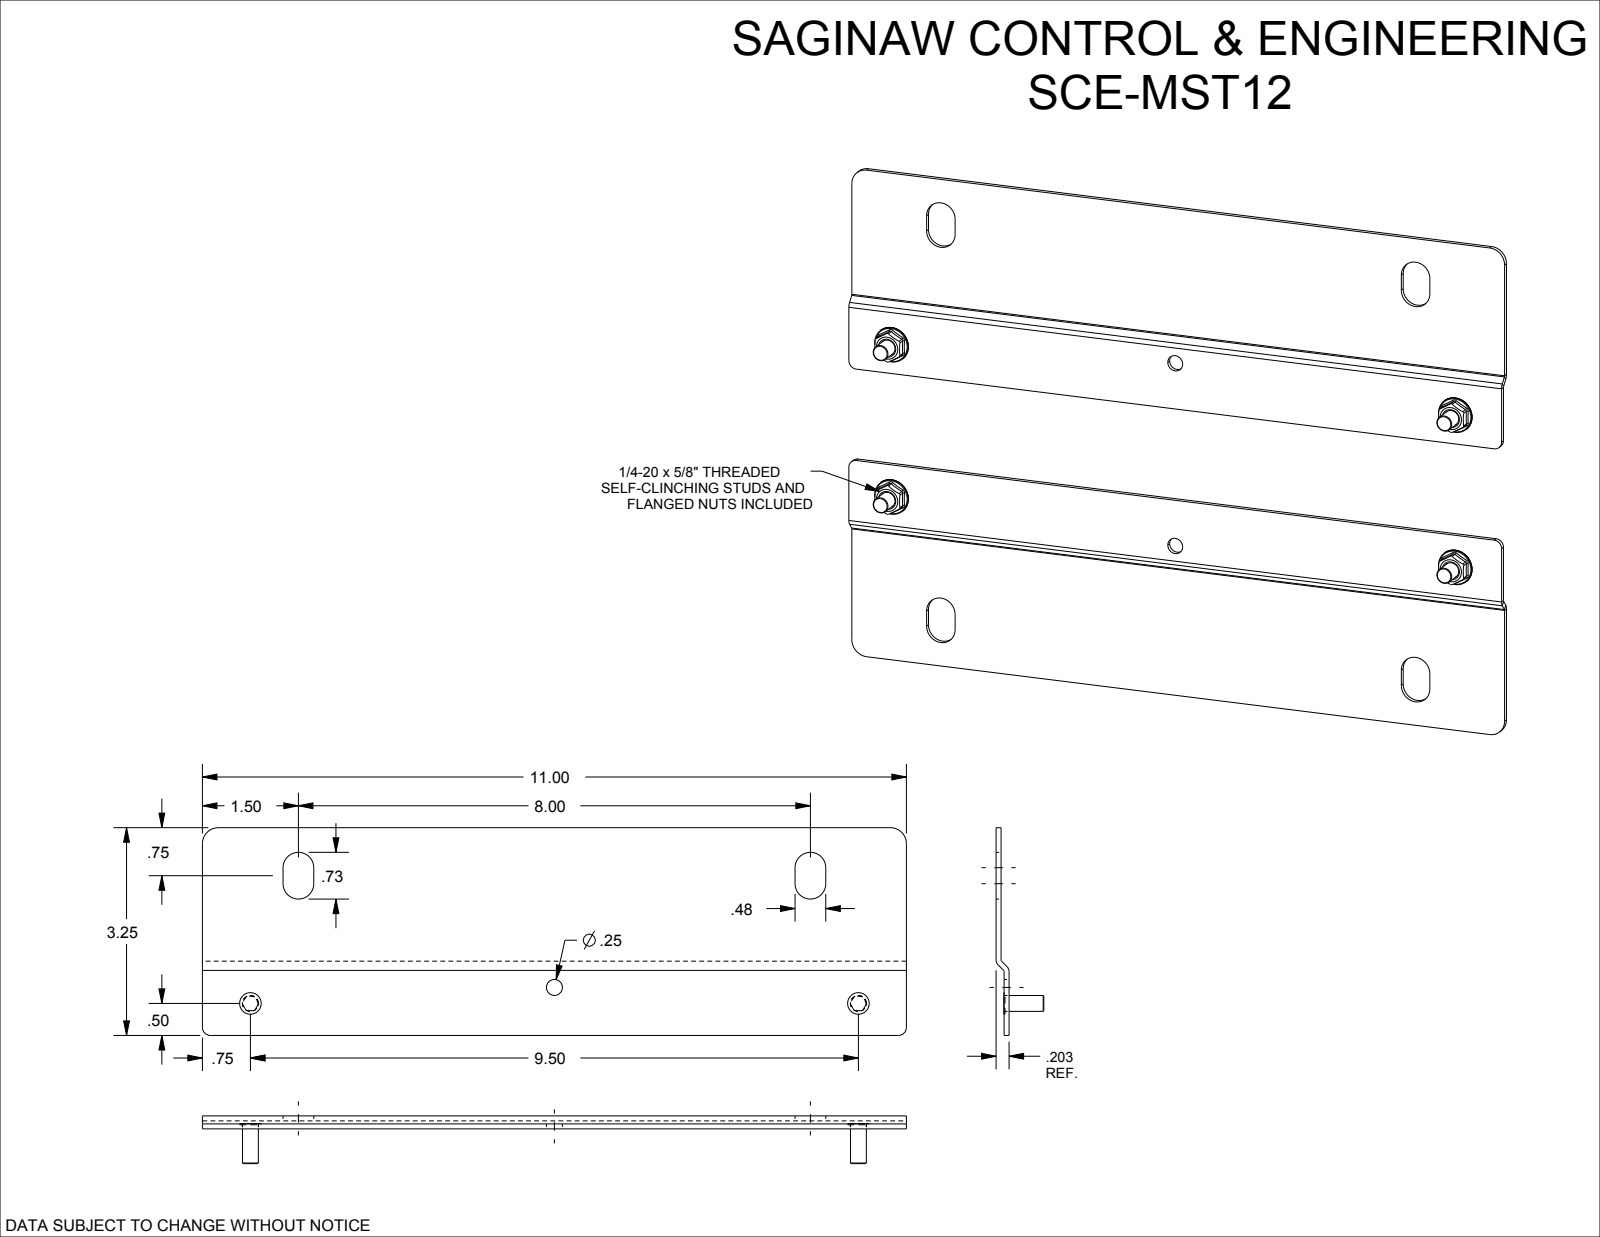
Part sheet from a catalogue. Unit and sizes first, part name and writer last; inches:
Units: inches
Overall size (bounding box): 11 × 7.99 × 0.746
Round holes (diameter × count): ⌀0.25 ×6, ⌀0.25 ×4
Round bosses / shafts (diameter × count): ⌀0.563 ×4, ⌀0.337 ×4, ⌀0.248 ×4
Partial cylindrical surfaces — rounded edges, fillets, slot ends (radius × count): R0.029 ×24, R0.24 ×8, R0.023 ×4, R0.101 ×4, R0.125 ×4, R0.25 ×4
Main face-to-face distances: 0.078, 0.078, 0.125, 0.203, 0.047, 0.125, 3.245, 4.745, 1.5, 7.99
Hole centre spacings: 4.757, 5.489, 2.5, 9.5, 9.824, 3
Volume: 5.733 in³ · Surface area: 152.7 in²
Bodies: 10 solids, 1010 faces (332 planar, 70 cylindrical, 608 other)
Part name (STEP PRODUCT): SCE-MST12
STEP written by: SolidWorks 2019 (AUTOMOTIVE_DESIGN)
